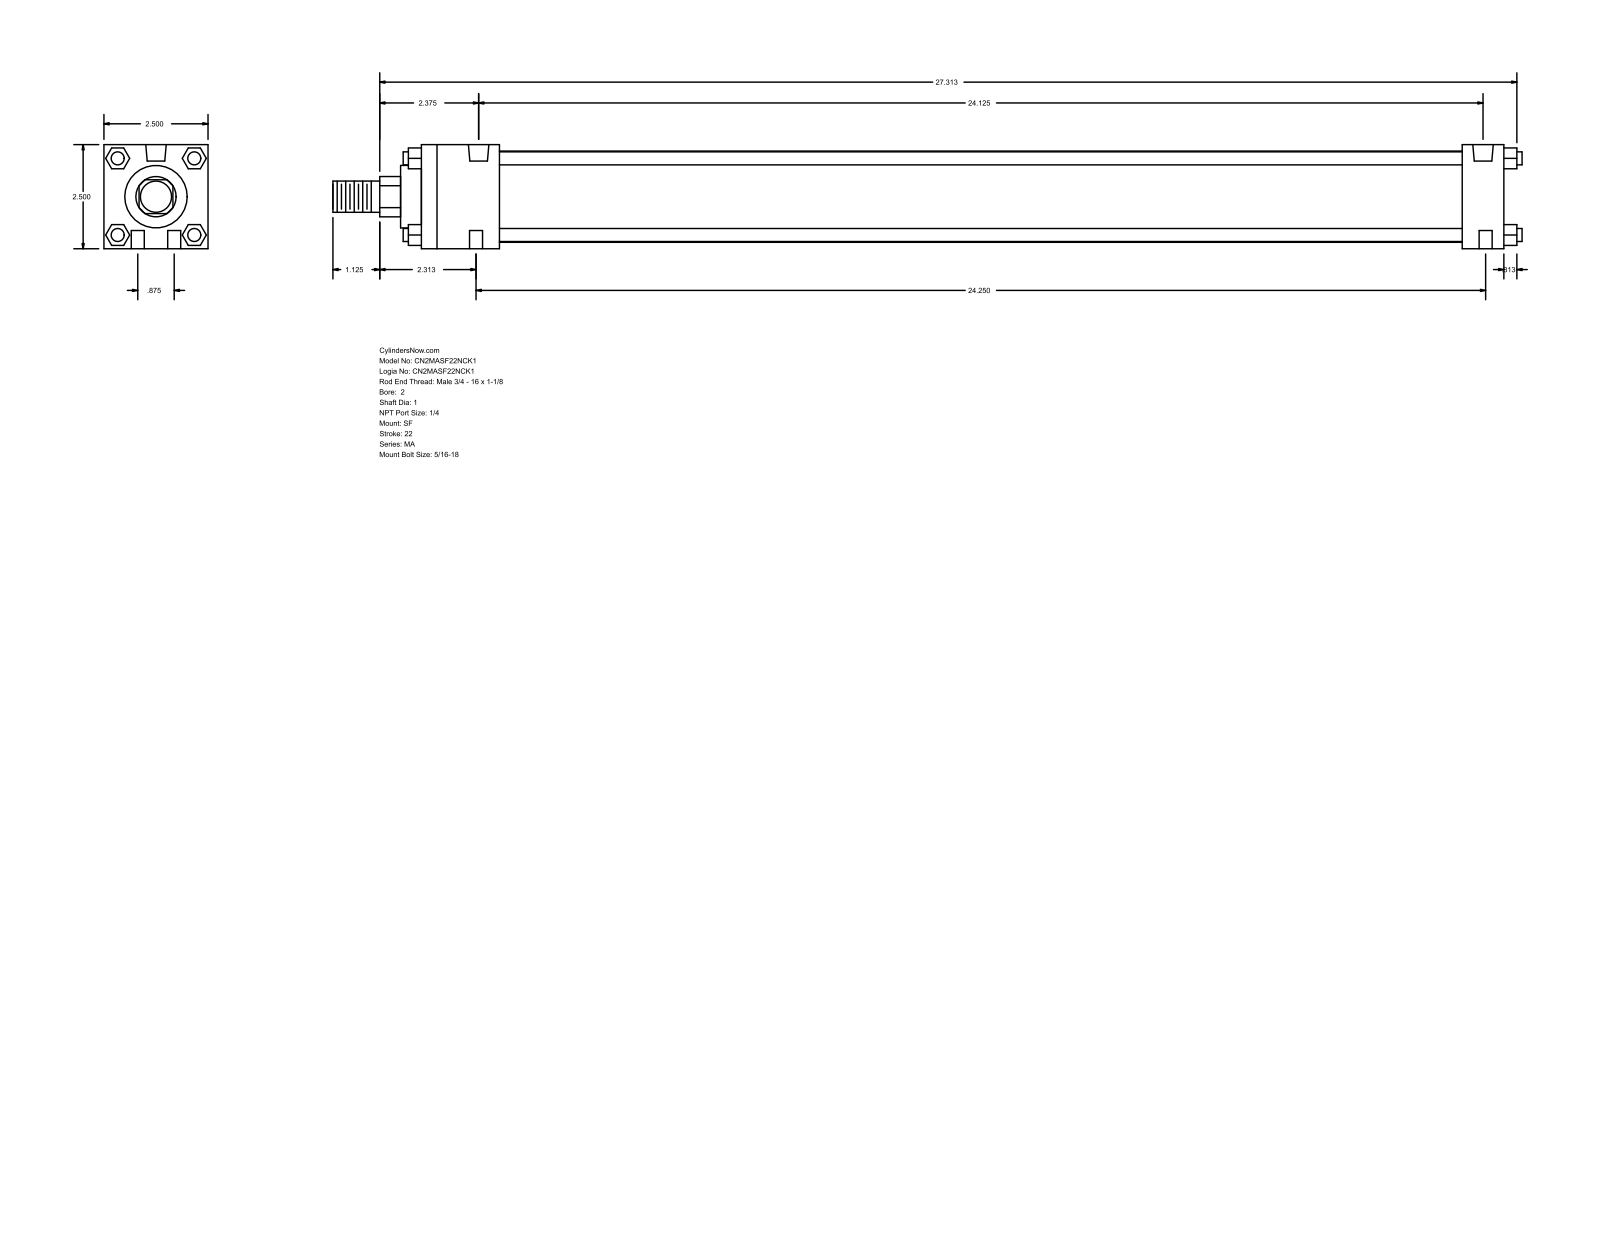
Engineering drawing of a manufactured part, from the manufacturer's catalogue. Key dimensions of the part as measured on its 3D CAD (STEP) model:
Part name (STEP PRODUCT): MA_SF__0200_1
STEP written by: GSSL Pune (CONFIG_CONTROL_DESIGN)
Units: millimetres
Bodies: 0 solids, 124 faces (94 planar, 30 cylindrical, 0 other)
Overall size (bounding box): 725.49 × 63.5 × 63.5
Round holes (diameter × count): ⌀7.94 ×6, ⌀12.49 ×2
Round bosses / shafts (diameter × count): ⌀7.94 ×4, ⌀55.63 ×1, ⌀38.1 ×1, ⌀25.4 ×1, ⌀19.05 ×1
Partial cylindrical surfaces — rounded edges, fillets, slot ends (radius × count): R12.29 ×1
Main face-to-face distances: 63.5, 660.4, 12.7, 25.4, 635, 47.63, 587.37, 612.77, 23.37, 40.47
Hole centre spacings: 11.22, 614.46, 22.22, 612.77, 615.95, 616.35
